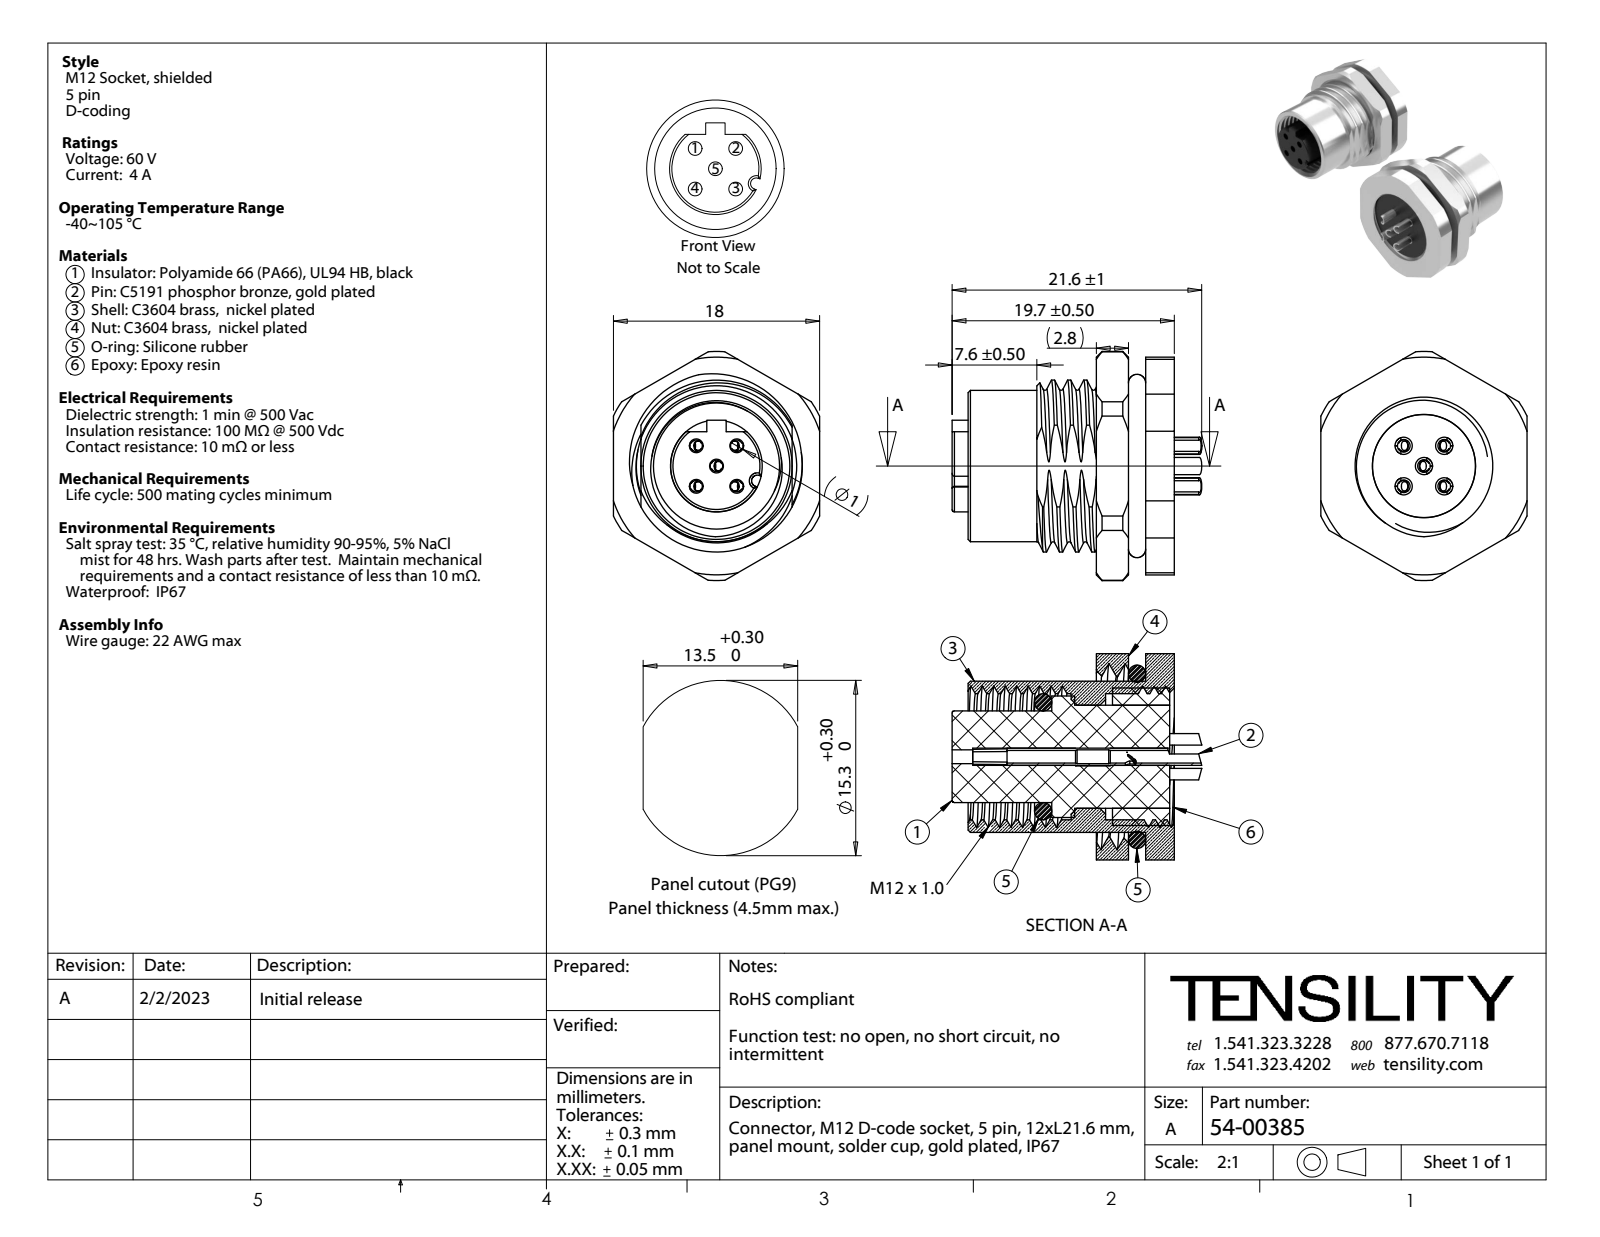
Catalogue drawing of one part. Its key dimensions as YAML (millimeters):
part_name: "54-00385-02; 54-00385-03; 54-00385-05; 54-00385-06 (+3 more)"
step_written_by: "SolidWorks 2021 (CONFIG_CONTROL_DESIGN)"
units: millimeters
bodies: {solids: 11, faces: 652, planar: 180, cylindrical: 216, other: 256}
overall_size: [21.8, 20, 18]
volume: 2888
surface_area: 5660
round_holes:
  - {diameter: 1.1, count: 5}
  - {diameter: 1.2, count: 5}
  - {diameter: 9, count: 1}
  - {diameter: 11, count: 1}
  - {diameter: 14, count: 1}
round_bosses_or_shafts:
  - {diameter: 1.6, count: 5}
  - {diameter: 1.5, count: 5}
  - {diameter: 13.2, count: 1}
  - {diameter: 12, count: 1}
  - {diameter: 10.6, count: 1}
partial_cylinders:
  - {radius: 0.1, count: 10}
  - {radius: 0.4, count: 8}
  - {radius: 0.2, count: 2}
  - {radius: 0.5, count: 1}
  - {radius: 4, count: 1}
  - {radius: 7.5, count: 1}
  - {radius: 9.5, count: 1}
  - {radius: 10, count: 1}
face_to_face_distances: [18, 2.5, 1.4, 0.4, 2.1, 3.6, 4, 6.4, 1.5, 6.8]
hole_center_spacings: [2.5, 3.54, 5.01]
